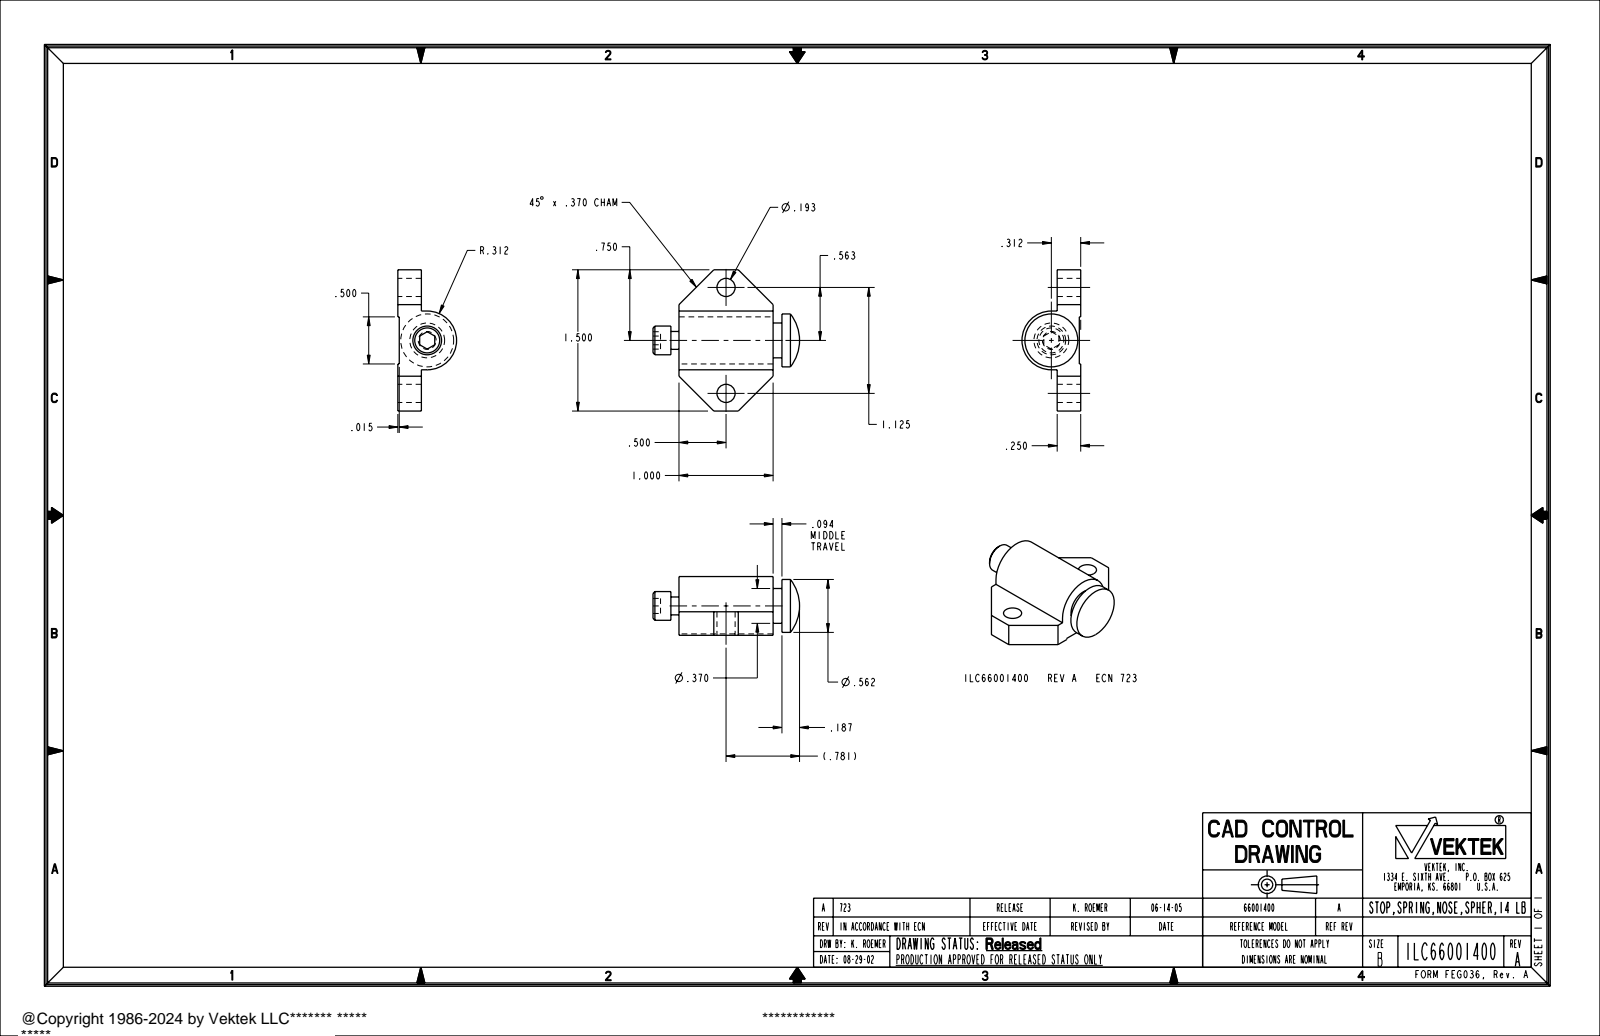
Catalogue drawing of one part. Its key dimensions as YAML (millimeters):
part_name: "ILC66001400"
step_written_by: "PRO/ENGINEER BY PARAMETRIC TECHNOLOGY CORPORATION, 2004290 (AUTOMOTIVE_DESIGN_CC2)"
units: millimeters
bodies: {solids: 1, faces: 44, planar: 27, cylindrical: 13, other: 4}
overall_size: [39.5, 38.1, 15.8]
volume: 8770
surface_area: 3538
round_holes:
  - {diameter: 4.9, count: 2}
round_bosses_or_shafts:
  - {diameter: 14.3, count: 1}
  - {diameter: 9.4, count: 1}
  - {diameter: 7.7, count: 1}
  - {diameter: 4.8, count: 1}
partial_cylinders:
  - {radius: 7.9, count: 1}
face_to_face_distances: [6.4, 0.4, 6, 25.4, 31.6, 2.4, 27.8, 11.1, 27, 38.1]
hole_center_spacings: [28.6]
